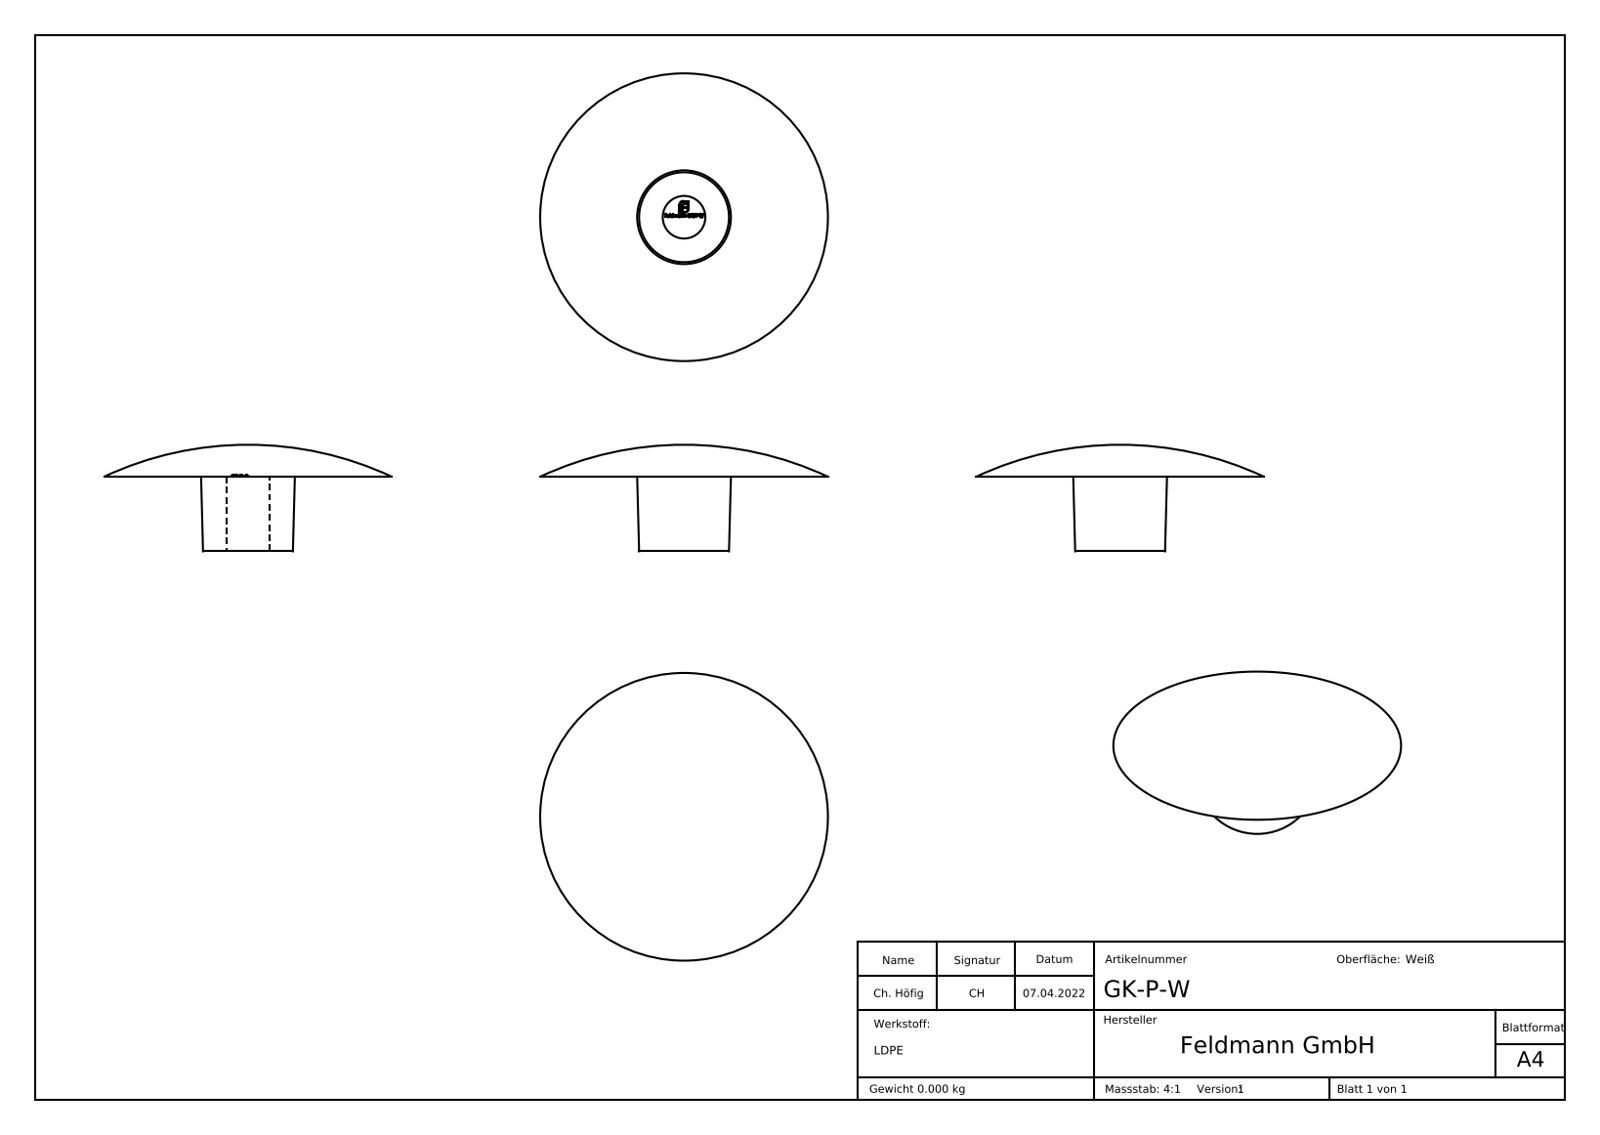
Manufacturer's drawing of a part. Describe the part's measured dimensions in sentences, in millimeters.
The part is named "GK-P-W". Its 3-D file was written by "SolidWorks 2018 (CONFIG_CONTROL_DESIGN)". It is 1 solid with 228 faces: 142 planar, 1 cylindrical and 85 other. Overall it measures 13.5 by 13.5 by 5 millimeters. Its volume is 149 cubic millimeters and its surface area 363 square millimeters. Round holes: 1 of diameter 2. The main face-to-face distances are 3.5, 3.6, 0.34, 0.4, 0.47, 0.36, 0.53, 0.45, 0.62, 0.73.
